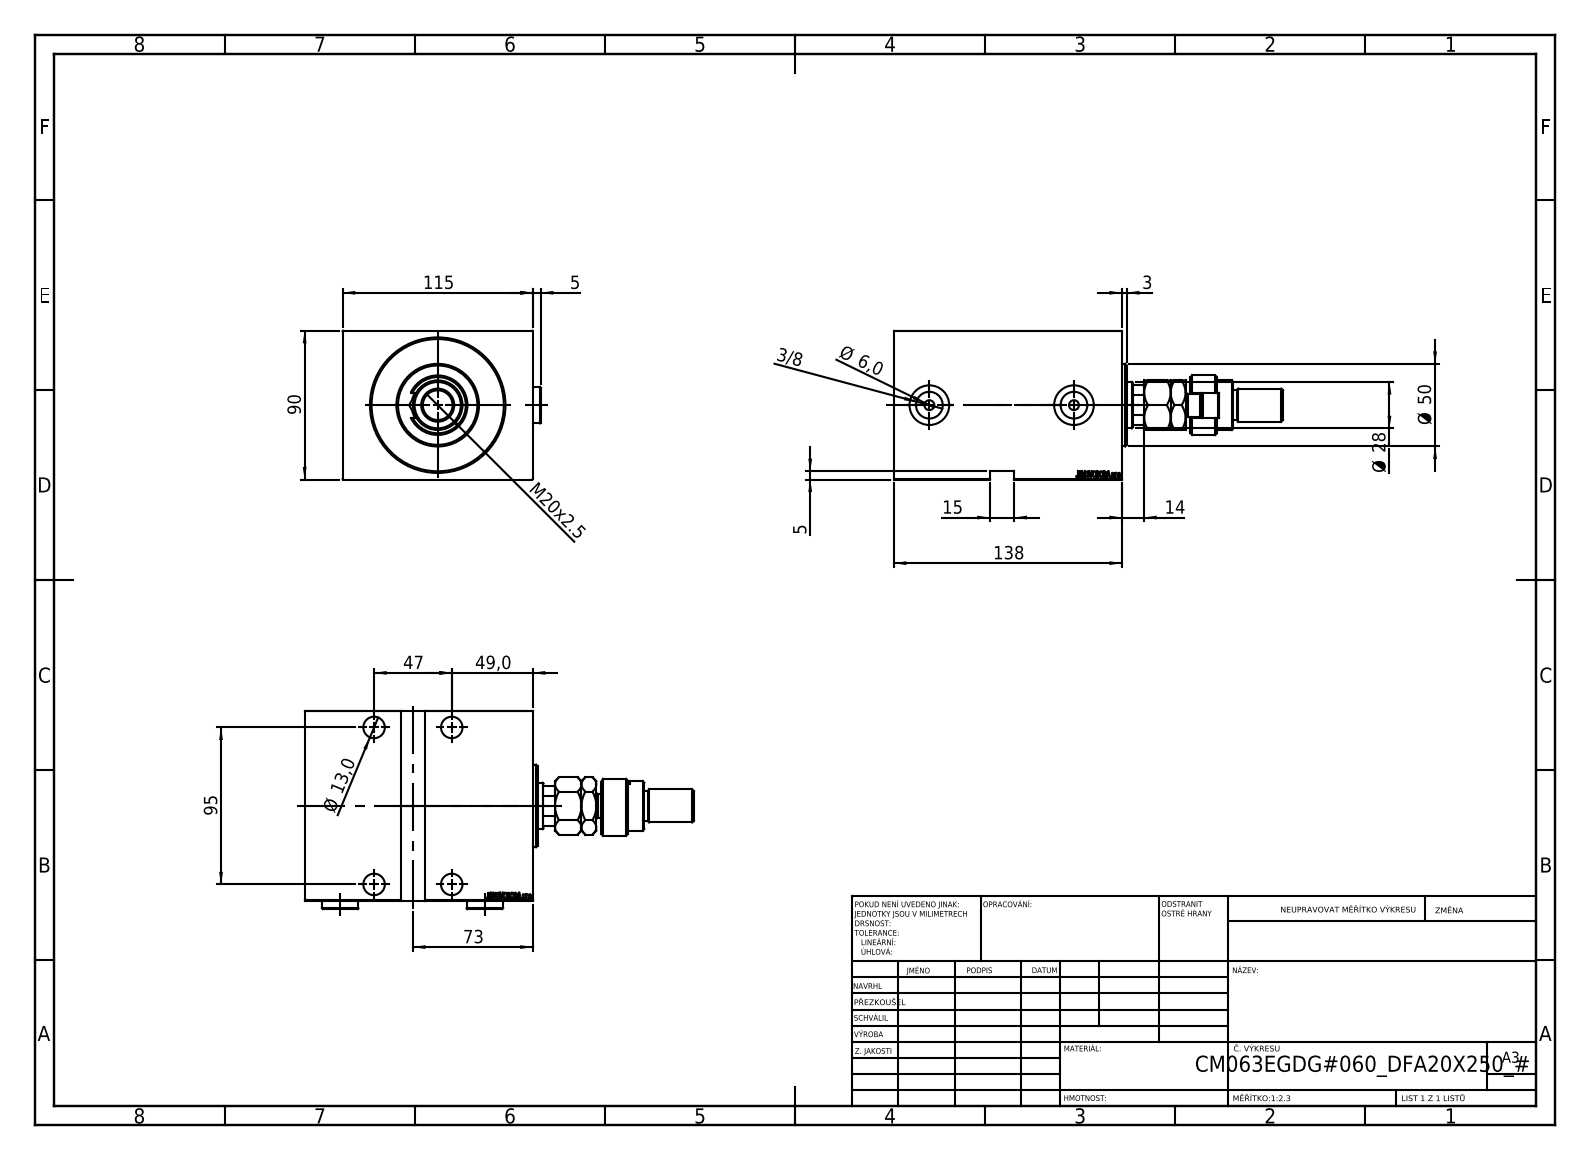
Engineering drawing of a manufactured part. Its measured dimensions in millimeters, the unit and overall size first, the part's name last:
Units: millimetres
Overall size (bounding box): 235.5 × 119.9 × 90
Round holes (diameter × count): ⌀13 ×4, ⌀19 ×4, ⌀6 ×2, ⌀16.17 ×2, ⌀24 ×2, ⌀18.5 ×1, ⌀28 ×1, ⌀31.5 ×1, ⌀63 ×1, ⌀80 ×1
Round bosses / shafts (diameter × count): ⌀22 ×3, ⌀65 ×1, ⌀50 ×1, ⌀36 ×1, ⌀30 ×1, ⌀20 ×1, ⌀18 ×1, ⌀14 ×1
Partial cylindrical surfaces — rounded edges, fillets, slot ends (radius × count): R7.5 ×1, R12 ×1, R13.5 ×1
Main face-to-face distances: 90, 115, 138, 17.5, 120.5, 5, 133, 115.5, 64.5, 121.4
Hole centre spacings: 47, 95, 105.99, 87.5
Volume: 1 262 000 mm³ · Surface area: 175 824 mm²
Bodies: 7 solids, 997 faces (474 planar, 81 cylindrical, 442 other)
Part name (STEP PRODUCT): MFA; FEMALE_PART_FOR_DFA; V450CM_E_VCP; V450CM_E_Body (+2 more)
STEP written by: SolidWorks 2019 (CONFIG_CONTROL_DESIGN)
